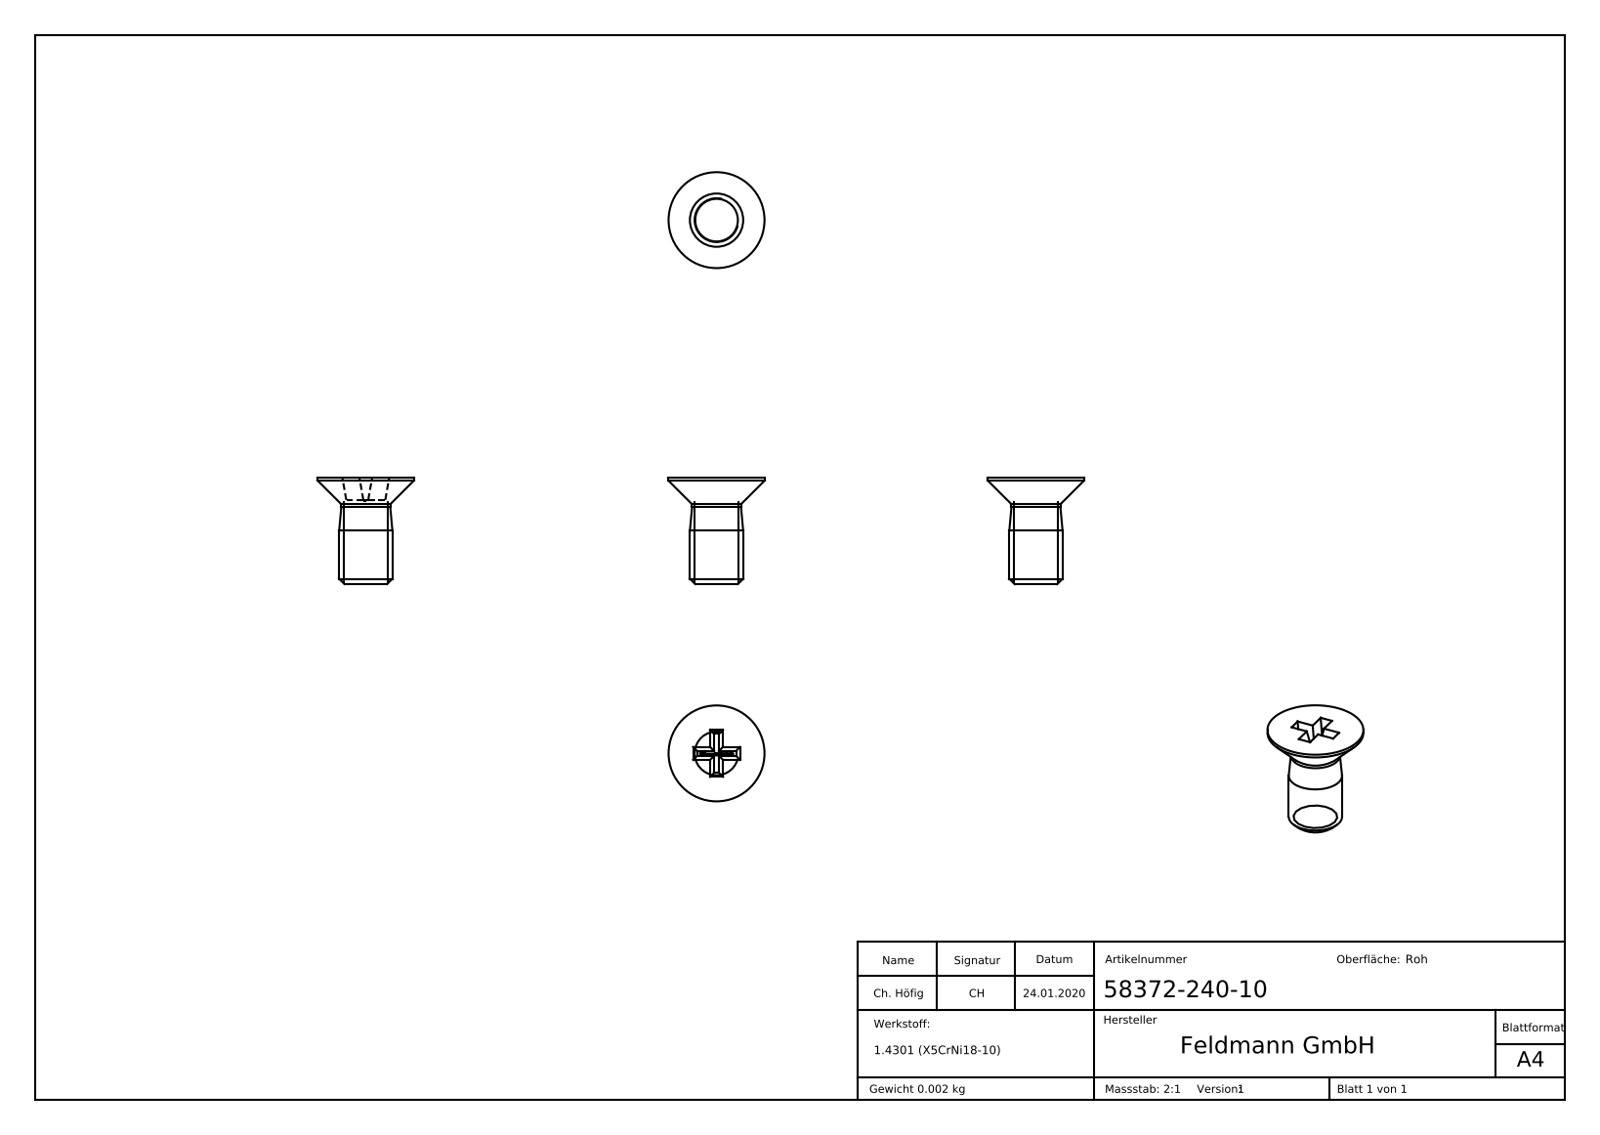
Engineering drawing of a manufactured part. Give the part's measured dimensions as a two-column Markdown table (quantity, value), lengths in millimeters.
| quantity | value |
| --- | --- |
| part name | 58372-240-10 |
| STEP written by | SolidWorks 2015 (CONFIG_CONTROL_DESIGN) |
| units | millimeters |
| bodies | 1 solid, 274 faces (151 planar, 3 cylindrical, 120 other) |
| overall size | 10 × 9 × 9 |
| volume | 230 mm³ |
| surface area | 300 mm² |
| round bosses / shafts (diameter × count) | 9 × 1, 5 × 1, 4.6 × 1 |
| main face-to-face distances | 10, 1.58, 7.9, 2.1, 7.8, 2.2, 0.36, 2.57, 0.31, 0.5 |
